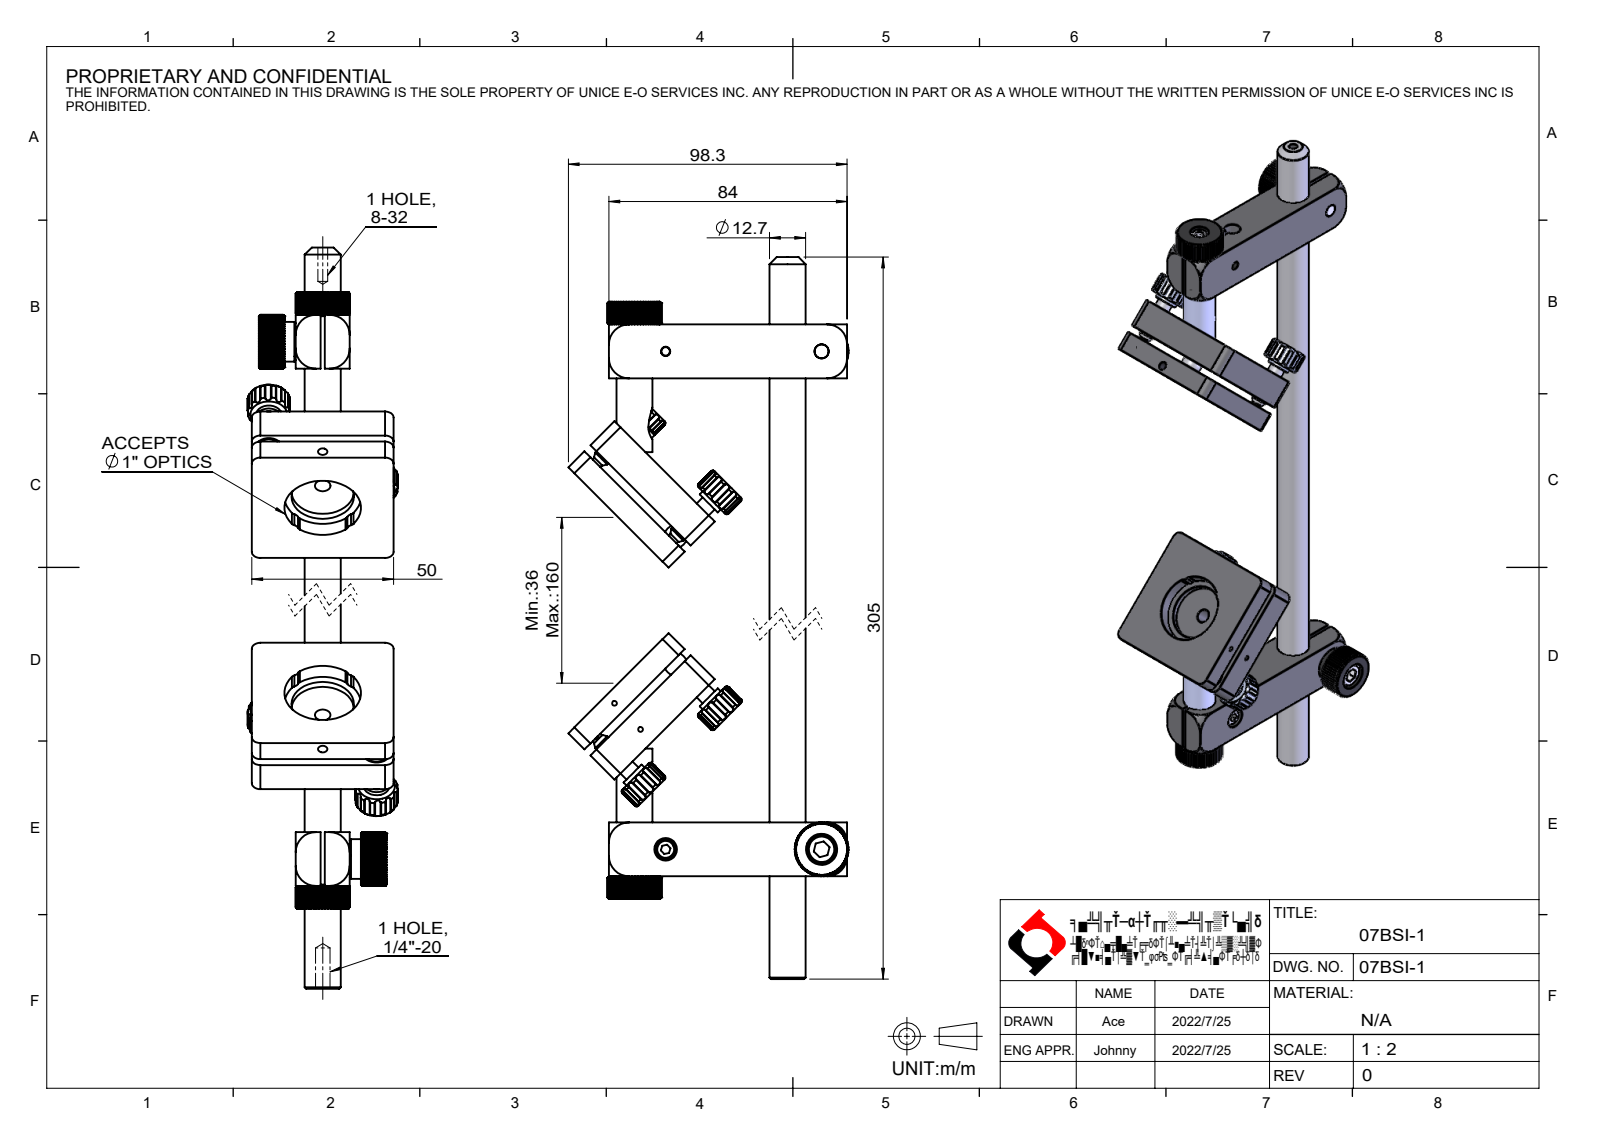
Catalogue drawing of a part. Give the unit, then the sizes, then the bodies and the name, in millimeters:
Units: millimetres
Overall size (bounding box): 305 × 98.82 × 52.97
Round holes (diameter × count): ⌀1.7 ×8, ⌀3.3 ×7, ⌀7 ×7, ⌀4 ×4, ⌀4.5 ×4, ⌀4.7 ×4, ⌀5.19 ×4, ⌀5.75 ×4, ⌀6.3 ×4, ⌀8 ×4, ⌀9.5 ×4, ⌀6.5 ×3
Round bosses / shafts (diameter × count): ⌀6 ×6, ⌀7 ×5, ⌀4 ×5, ⌀9.45 ×4, ⌀9 ×4, ⌀1.5 ×4, ⌀14 ×2, ⌀10 ×2
Partial cylindrical surfaces — rounded edges, fillets, slot ends (radius × count): R0.3 ×96, R1.5 ×50, R3 ×14, R0.75 ×8, R2 ×8, R2.5 ×4, R7.5 ×4, R9.5 ×3
Main face-to-face distances: 19, 8, 3, 11, 15.5, 34.5, 226.05, 12, 11.99, 14.99
Hole centre spacings: 13, 26.87, 19.92, 45.49, 19.93, 100.9, 15, 19.42
Volume: 200 240 mm³ · Surface area: 86 215 mm²
Bodies: 45 solids, 2146 faces (732 planar, 766 cylindrical, 648 other)
Part name (STEP PRODUCT): 07BSI-1
STEP written by: SolidWorks 2021 (CONFIG_CONTROL_DESIGN)
